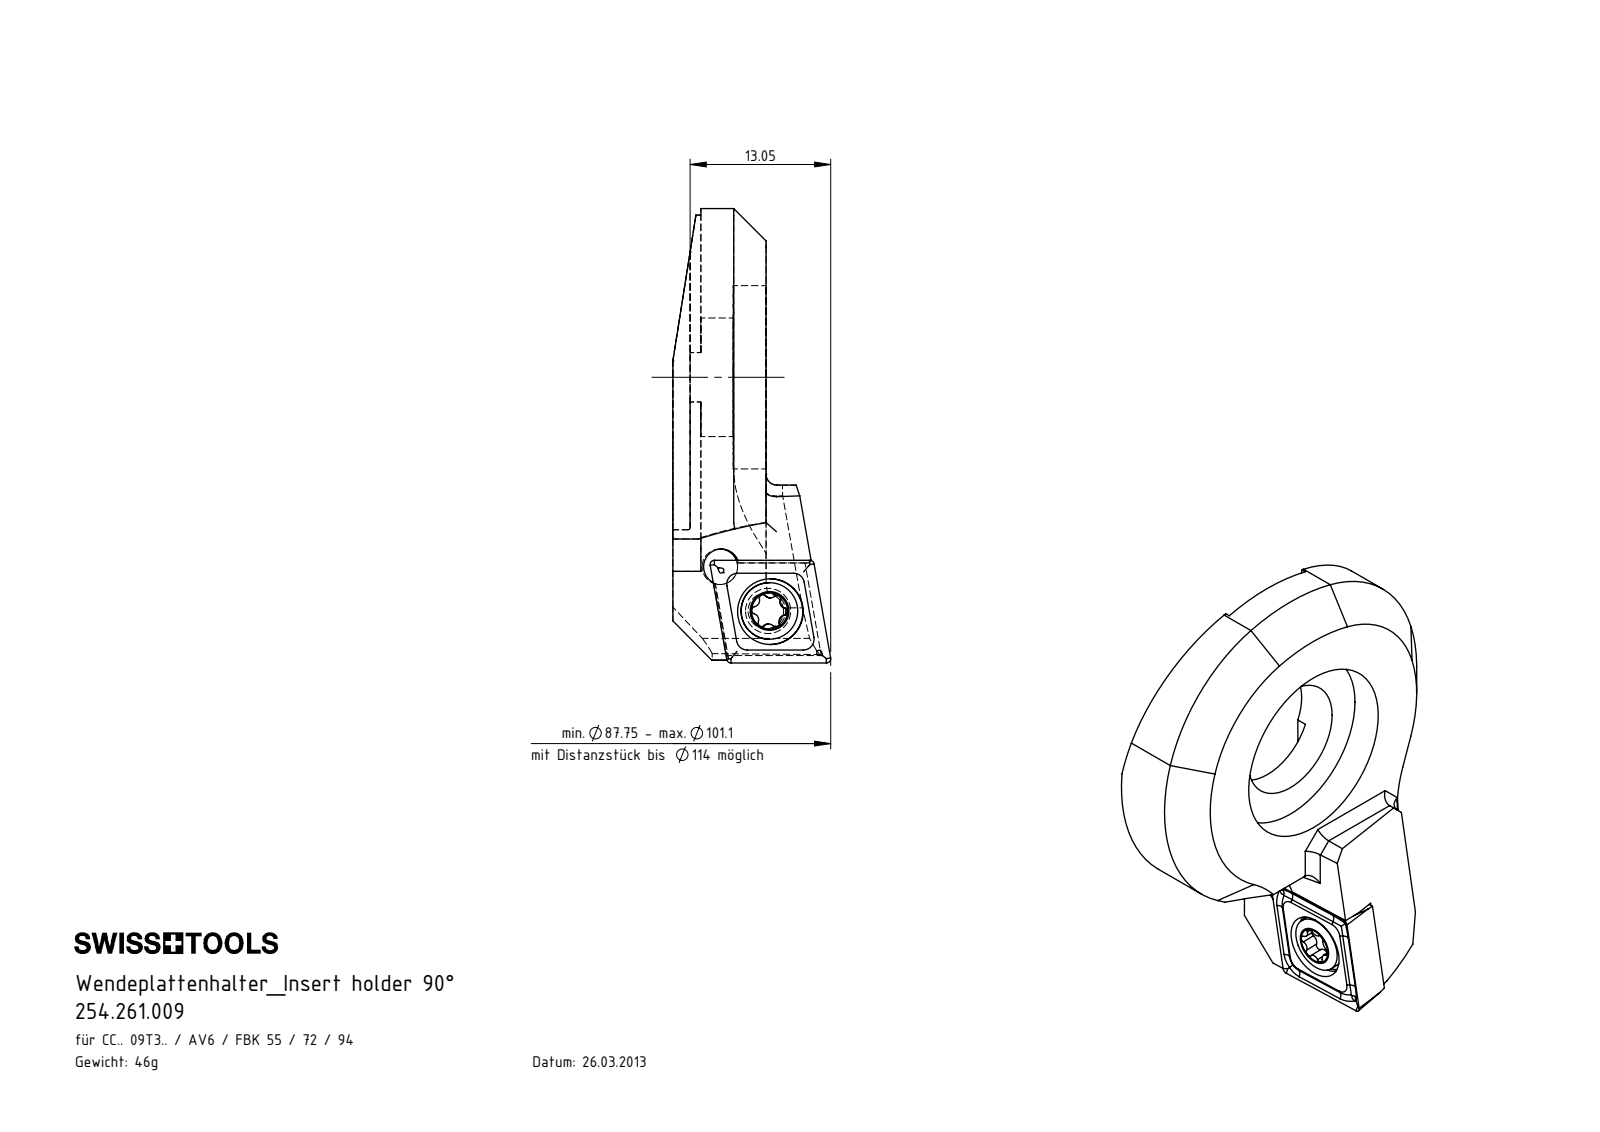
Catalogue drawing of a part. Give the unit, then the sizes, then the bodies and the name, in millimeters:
Units: millimetres
Overall size (bounding box): 42.15 × 33.1 × 14.65
Round holes (diameter × count): ⌀3.3 ×2, ⌀4.4 ×1, ⌀6.1 ×1, ⌀11 ×1, ⌀17 ×1
Round bosses / shafts (diameter × count): ⌀5.25 ×1, ⌀4 ×1
Partial cylindrical surfaces — rounded edges, fillets, slot ends (radius × count): R0.34 ×6, R0.59 ×6, R1 ×5, R15 ×3, R3.2 ×2, R16.55 ×1, R20.95 ×1, R40 ×1
Main face-to-face distances: 7.05, 1, 6.05, 8.65, 2.6, 1.6, 3, 3.05, 4, 5.6
Hole centre spacings: 6.07, 6.17
Volume: 5 814 mm³ · Surface area: 3 632 mm²
Bodies: 3 solids, 136 faces (51 planar, 37 cylindrical, 48 other)
Part name (STEP PRODUCT): WCB-ER2.001.009_A; AV6-WCB.001.013_A_fertigbearbeitet; AV6.WCB.001.013; CCMT09T304
STEP written by: SolidWorks 2017 (AUTOMOTIVE_DESIGN)
